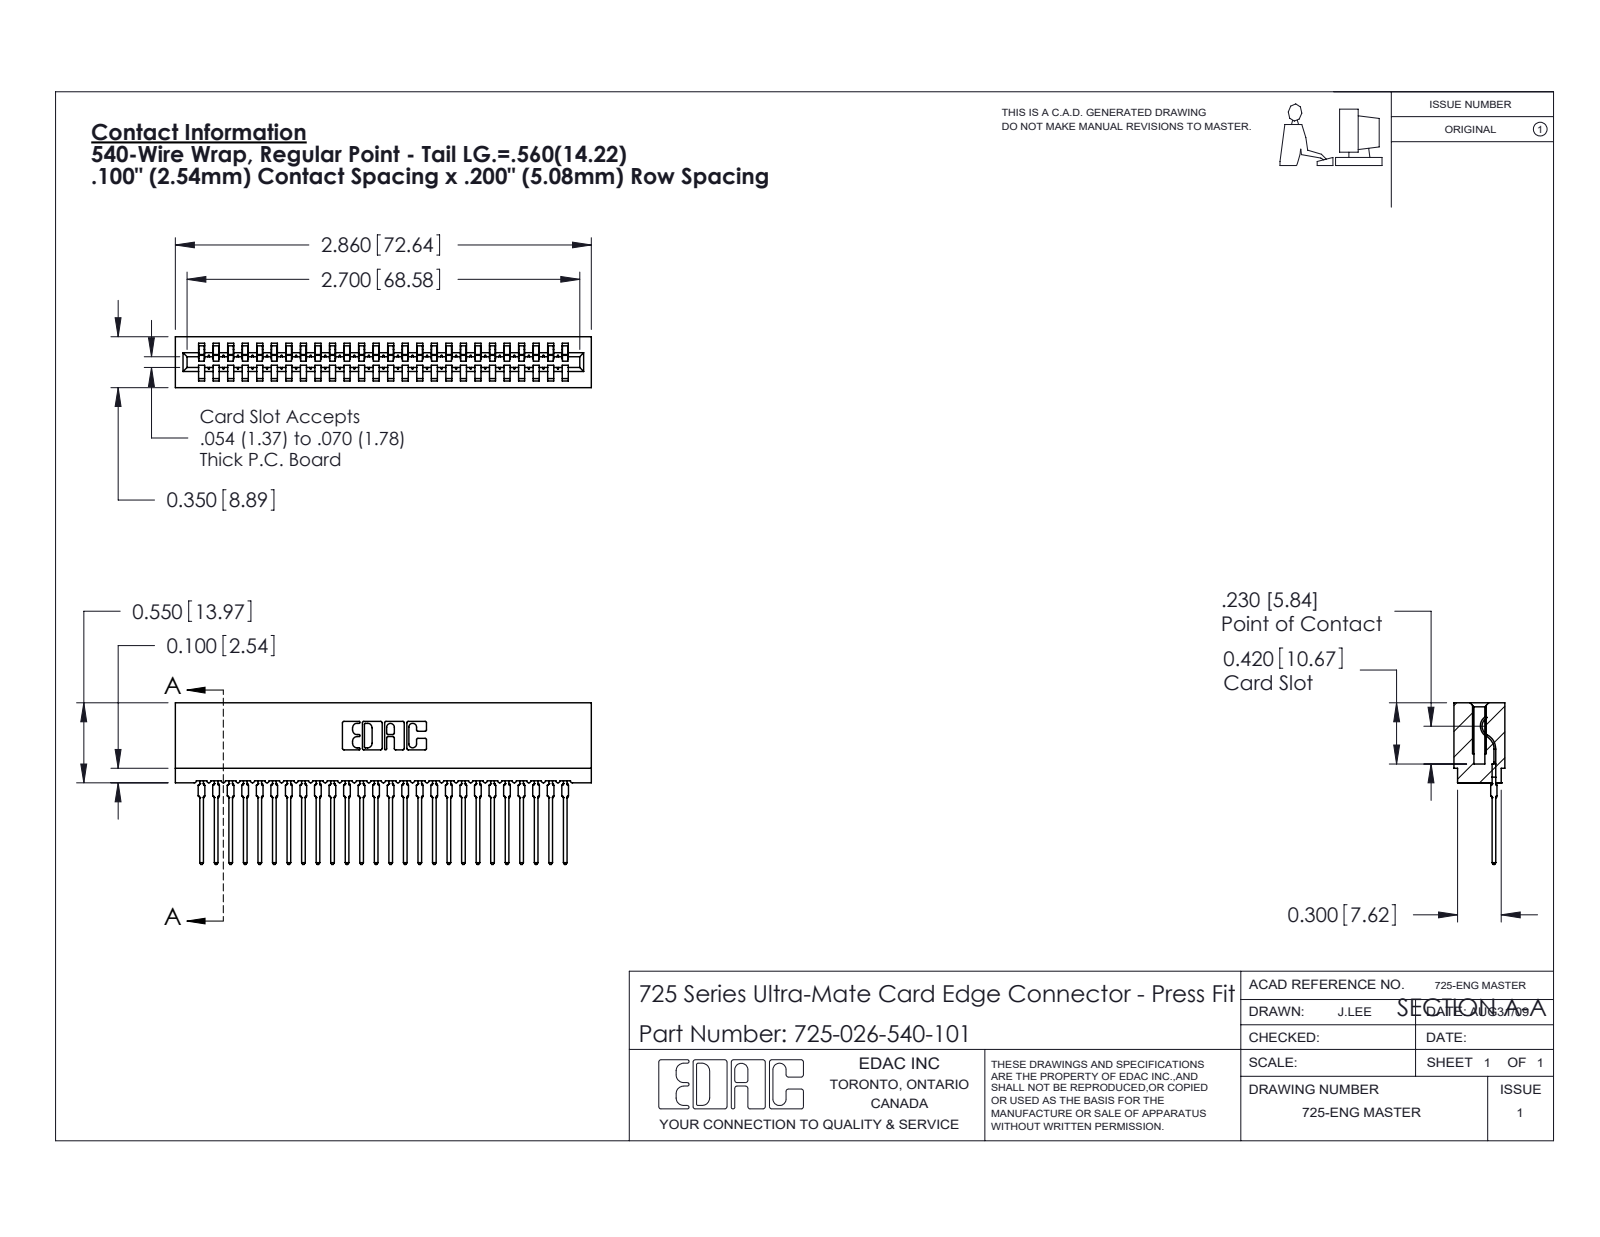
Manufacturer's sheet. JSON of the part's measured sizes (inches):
{"part_name": "725 Part_Insulator Option - 01; 745-292-001_540; 725-026-540-101", "step_written_by": "SolidWorks 2020 (CONFIG_CONTROL_DESIGN)", "units": "inches", "bodies": {"solids": 27, "faces": 3007, "planar": 1797, "cylindrical": 534, "other": 676}, "overall_size": [2.86, 1.111, 0.35], "volume_in3": 0.346, "surface_area_in2": 16.89, "partial_cylinders_radius": [[0.015, 52], [0.021, 52], [0.01, 22], [0.007, 6], [0.031, 6], [0.005, 4], [0.011, 4], [0.026, 3]], "face_to_face_distances": [0.2, 0.1, 0.3, 0.4, 0.35, 0.5, 0.6, 0.212, 0.138, 0.7]}
